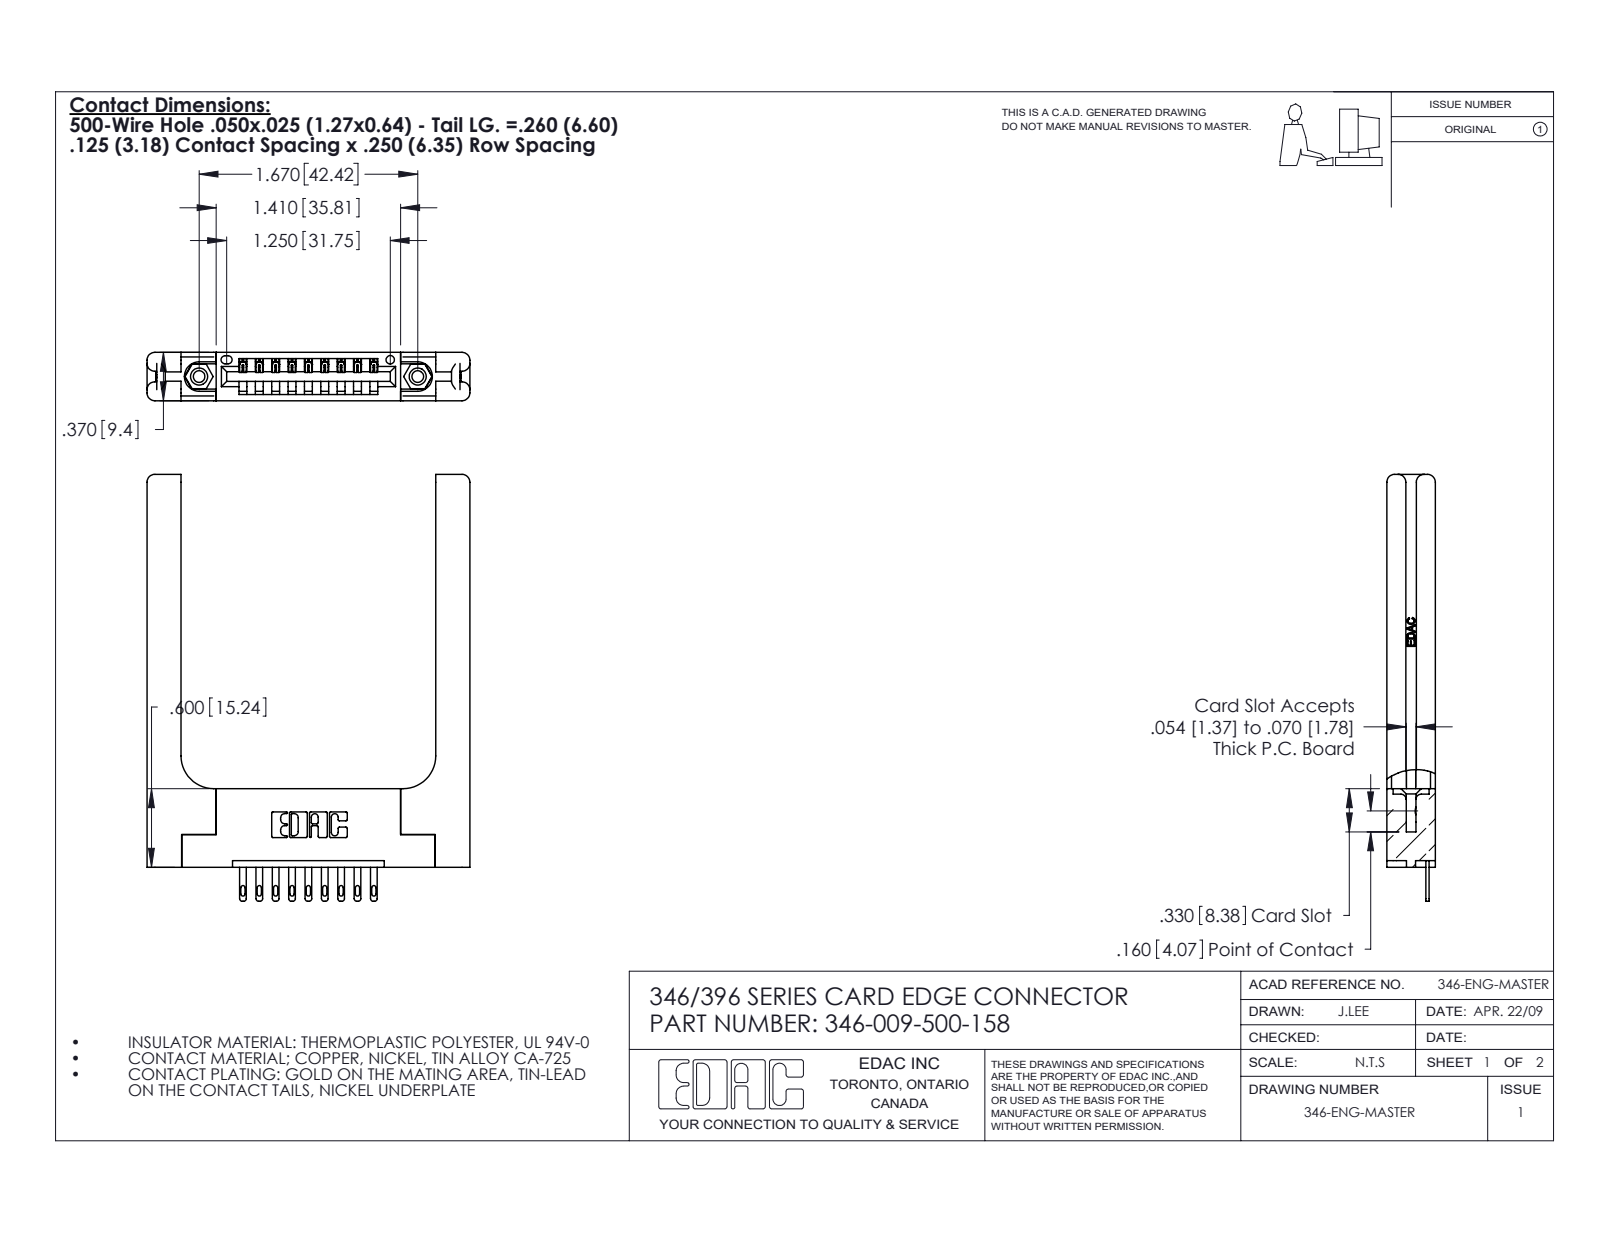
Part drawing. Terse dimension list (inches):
name: 346-220-058_345-220-058; 346 Part_Flush Mounting Lugs - 0.156 Dia-TH; 346-009-500-158; 345-250-001_345-250-001-102 (+1 more)
written by: SolidWorks 2020 (CONFIG_CONTROL_DESIGN)
unit: in
bodies: 14 solids, 878 faces (544 planar, 274 cylindrical, 60 other)
size: 3.26 × 2.466 × 0.37
volume: 0.81 in³; area: 18.69 in²
holes: 2× ⌀0.089, 2× ⌀0.125, 2× ⌀0.156, 1× ⌀0.064
bosses: 2× ⌀0.155
rounds: 22× R0.01, 18× R0.006, 18× R0.016, 18× R0.02, 16× R0.06, 6× R0.007, 6× R0.031, 3× R0.026
face distances: 0.37, 0.15, 0.072, 0.22, 0.148, 0.102, 0.25, 0.048, 0.322, 0.173
hole spacings: 0.246, 1.465, 1.67
